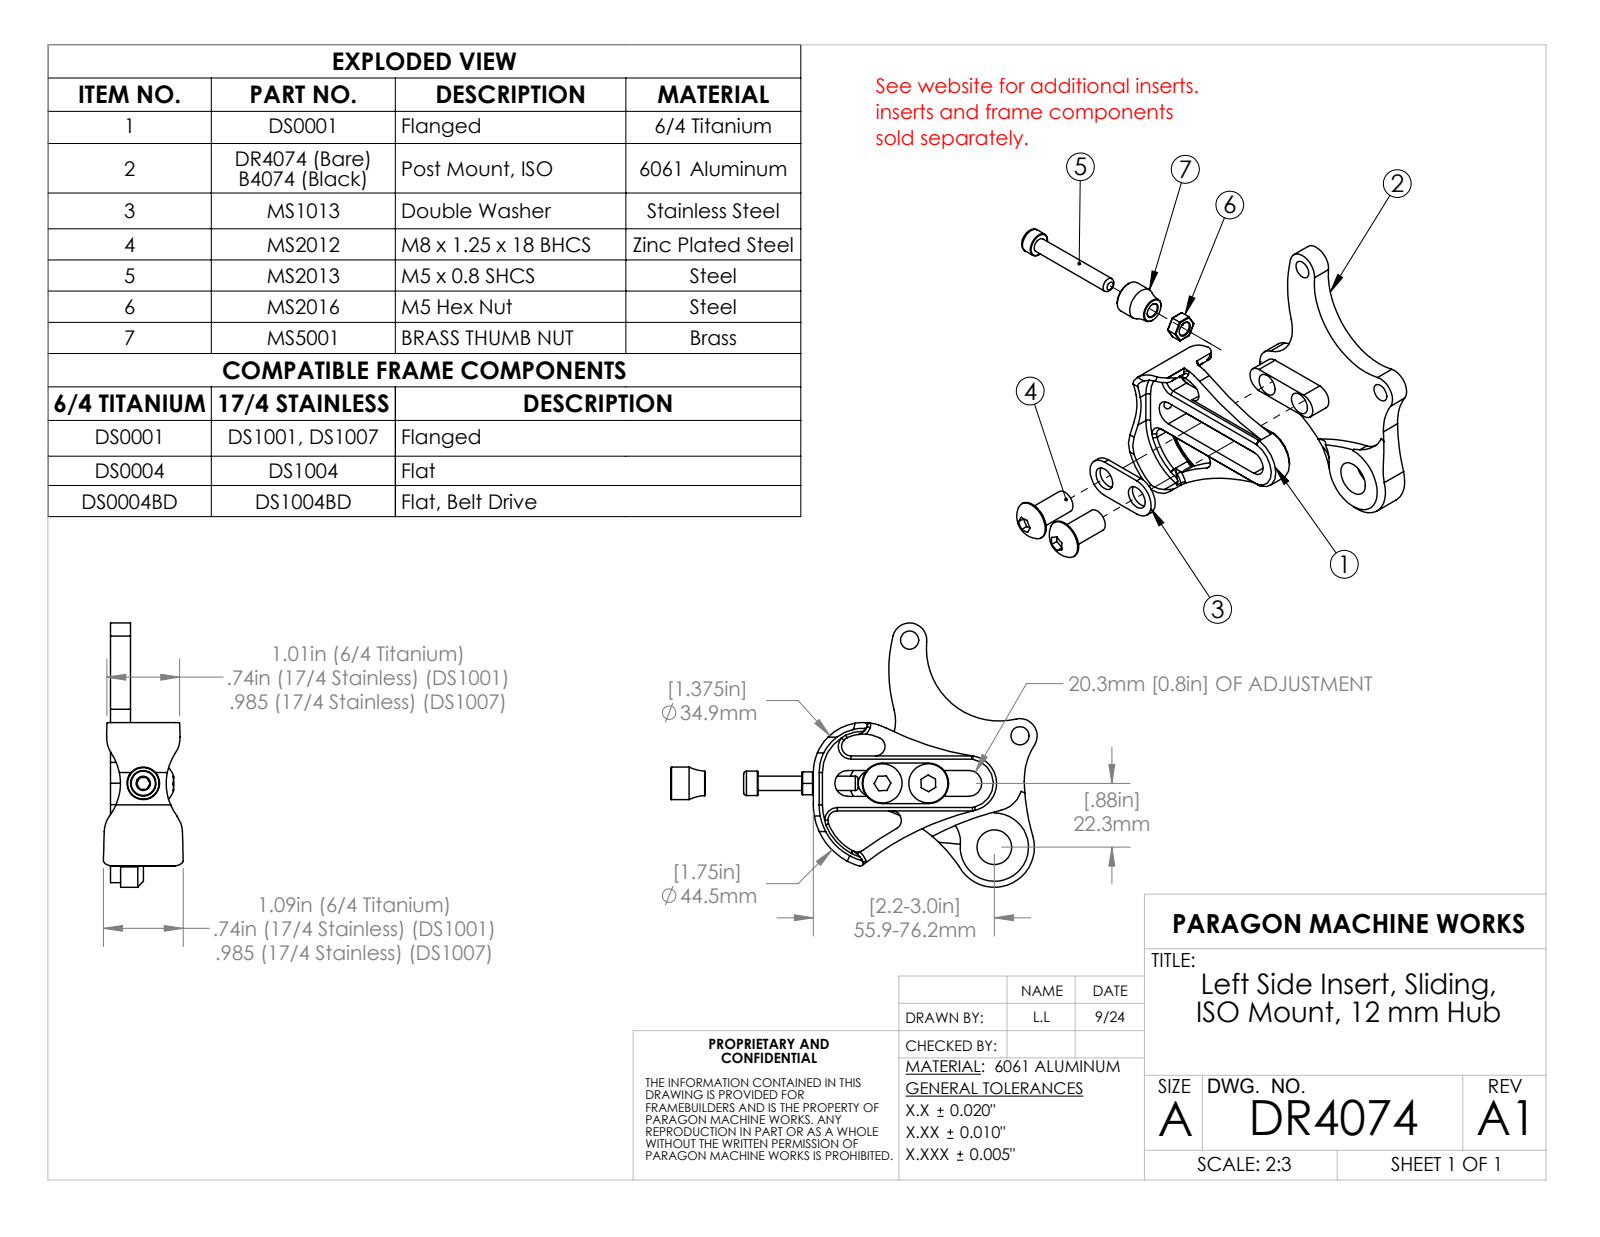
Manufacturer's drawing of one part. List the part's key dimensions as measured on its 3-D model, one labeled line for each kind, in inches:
Part name (STEP PRODUCT): MS2016; DS0001; MS5001; MS2012 (+4 more)
STEP written by: SolidWorks 2023 (AUTOMOTIVE_DESIGN)
Units: inches
Bodies: 8 solids, 274 faces (78 planar, 119 cylindrical, 77 other)
Overall size (bounding box): 7.535 × 4.868 × 3.633
Volume: 2.33 in³ · Surface area: 33.55 in²
Round holes (diameter × count): ⌀0.25 ×2, ⌀0.312 ×2, ⌀0.327 ×2, ⌀0.166 ×1, ⌀0.197 ×1, ⌀0.335 ×1, ⌀0.477 ×1
Round bosses / shafts (diameter × count): ⌀0.539 ×2, ⌀0.315 ×2, ⌀0.449 ×1
Partial cylindrical surfaces — rounded edges, fillets, slot ends (radius × count): R0.01 ×12, R0.13 ×4, R0.178 ×4, R0.375 ×4, R0.04 ×2, R0.045 ×2, R0.2 ×2, R0.236 ×2
Main face-to-face distances: 0.274, 1.774, 1.5, 2.128, 1.854, 0.354, 0.356, 0.453, 0.179, 1.321
Hole centre spacings: 0.63, 1.262, 1.419, 1.5, 1.571, 1.77, 1.985, 2
